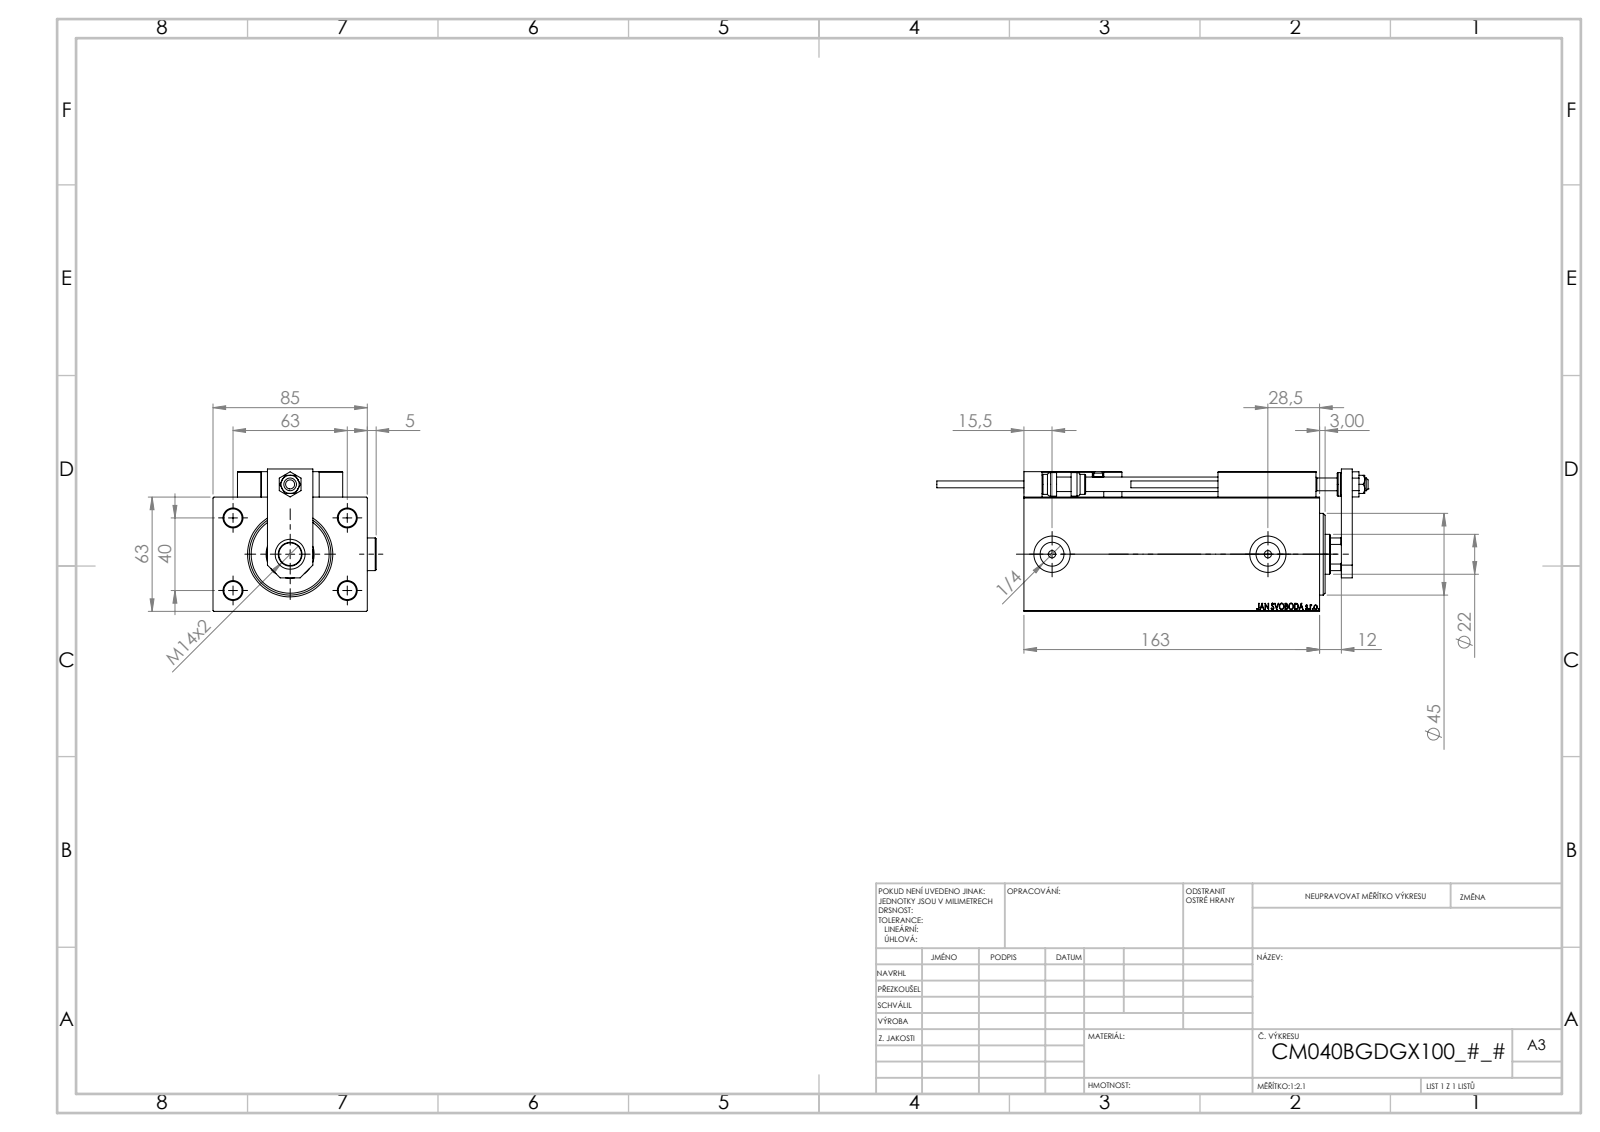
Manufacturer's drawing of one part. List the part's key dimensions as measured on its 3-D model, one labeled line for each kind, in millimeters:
Part name (STEP PRODUCT): SWITCH_X_FRONT_BACK; V450CM_B_VCP; SWITCH X; V450CM_VC_B (+7 more)
STEP written by: SolidWorks 2019 (CONFIG_CONTROL_DESIGN)
Units: millimetres
Bodies: 26 solids, 1372 faces (595 planar, 200 cylindrical, 577 other)
Overall size (bounding box): 237.7 × 89.9 × 78.5
Volume: 824 034 mm³ · Surface area: 136 156 mm²
Round holes (diameter × count): ⌀4 ×6, ⌀8 ×5, ⌀3.2 ×4, ⌀10 ×4, ⌀5 ×2, ⌀13.16 ×2, ⌀20 ×2, ⌀7 ×1, ⌀12.5 ×1, ⌀16.5 ×1, ⌀22 ×1, ⌀25.5 ×1
Round bosses / shafts (diameter × count): ⌀18 ×2, ⌀5 ×2, ⌀3.8 ×2, ⌀13 ×1, ⌀11 ×1
Partial cylindrical surfaces — rounded edges, fillets, slot ends (radius × count): R0.3 ×30, R3 ×2, R10.5 ×1
Main face-to-face distances: 63, 85, 12, 163, 151, 14, 77, 18, 30, 13.5
Hole centre spacings: 37.31, 11.37, 20, 29.59, 29.69, 36.06, 36.53, 40
